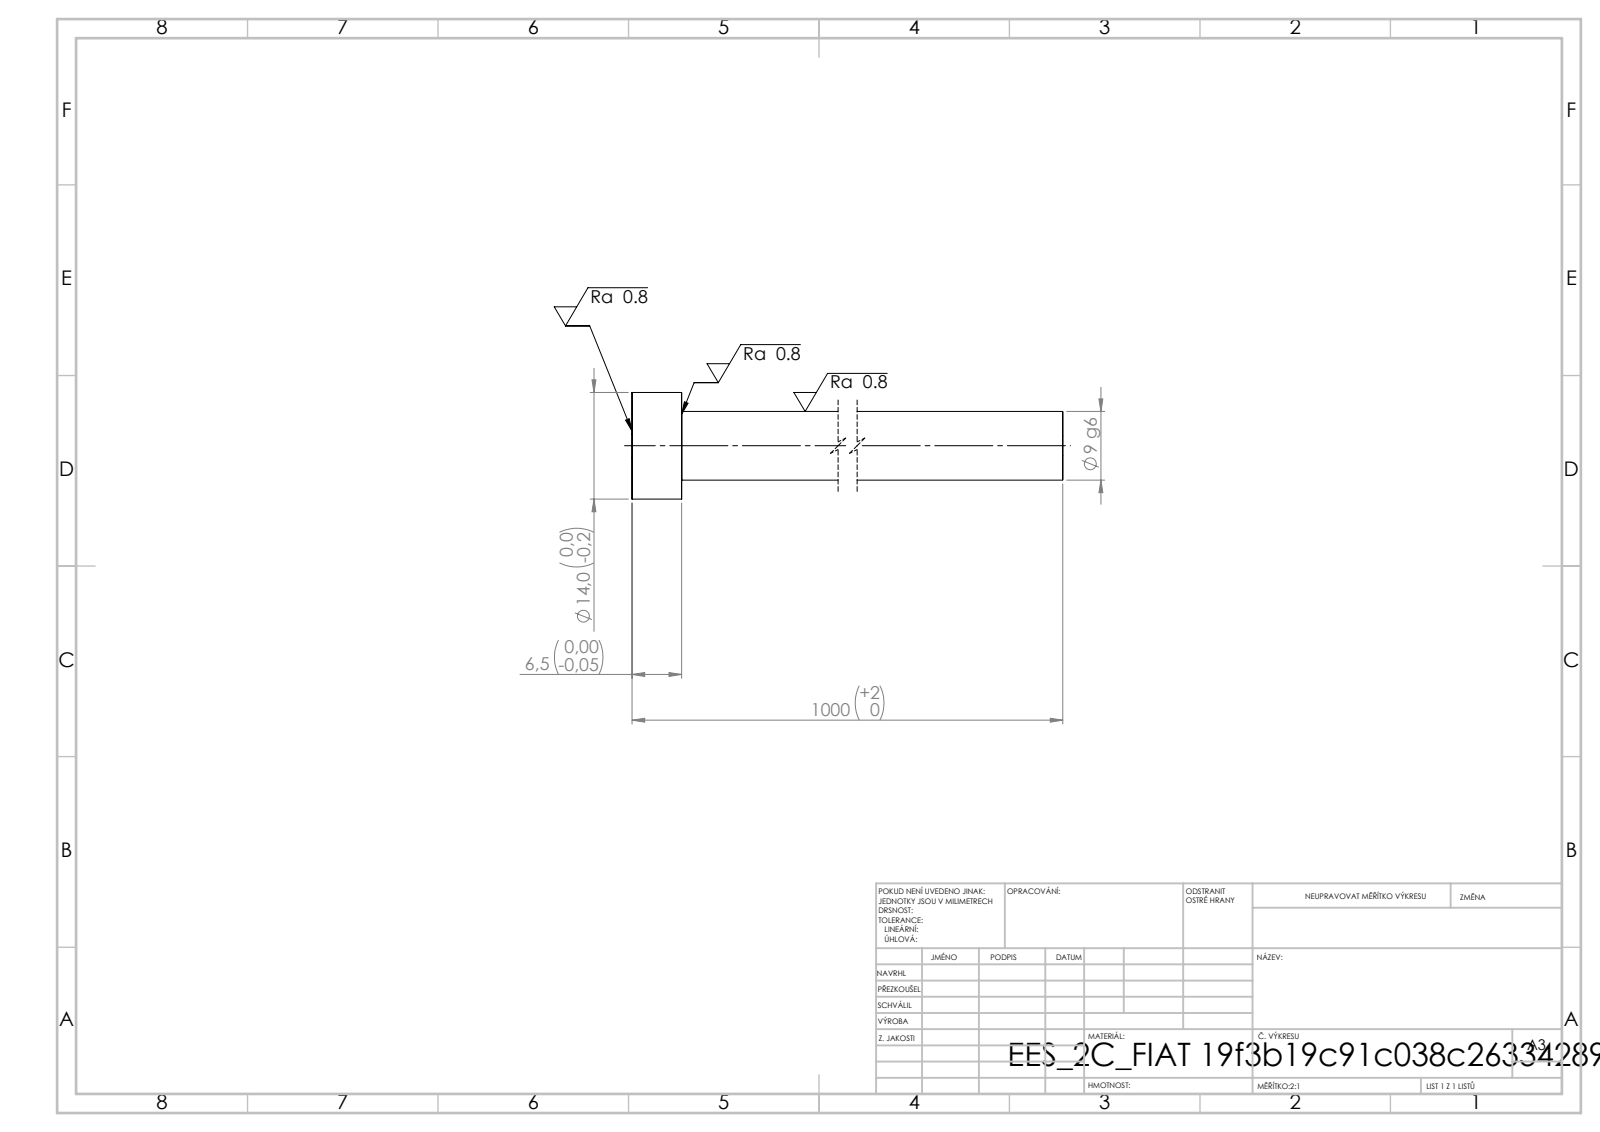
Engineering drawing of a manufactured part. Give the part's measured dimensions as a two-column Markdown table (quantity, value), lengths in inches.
| quantity | value |
| --- | --- |
| STEP written by | SolidWorks 2019 (CONFIG_CONTROL_DESIGN) |
| units | inches |
| bodies | 1 solid, 7 faces (3 planar, 4 cylindrical, 0 other) |
| overall size | 39.37 × 0.551 × 0.551 |
| volume | 3.918 in³ |
| surface area | 44.46 in² |
| round bosses / shafts (diameter × count) | 0.551 × 1, 0.354 × 1 |
| main face-to-face distances | 0.256, 39.37, 39.114 |
